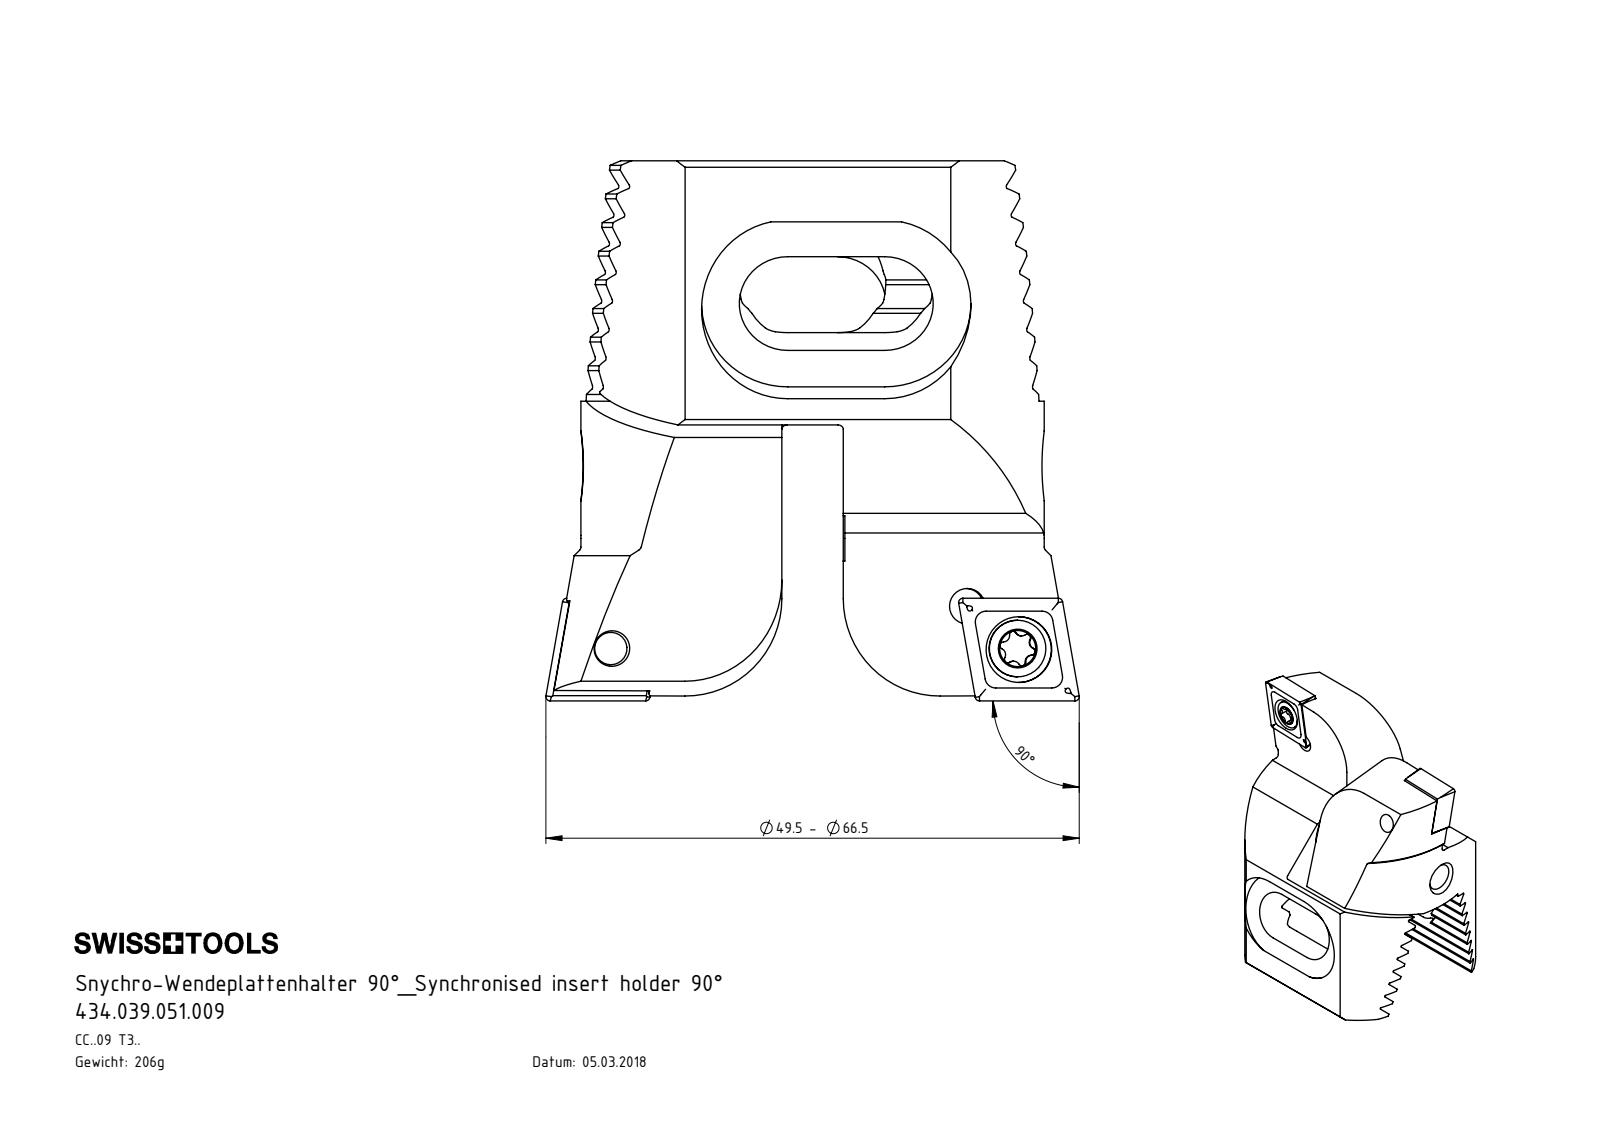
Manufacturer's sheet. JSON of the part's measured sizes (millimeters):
{"part_name": "Z42-ER3.001.040_A; Z42-ER3.000.040; 434.039.051.009; Z42-ER3.002.005_A (+4 more)", "step_written_by": "SolidWorks 2017 (CONFIG_CONTROL_DESIGN)", "units": "millimeters", "bodies": {"solids": 11, "faces": 525, "planar": 205, "cylindrical": 170, "other": 150}, "overall_size": [50.1, 49.5, 34.2], "volume_mm3": 27942, "surface_area_mm2": 14559, "round_holes": [[3.3, 7], [1, 2], [4.4, 2], [6.1, 2], [5, 1]], "round_bosses_or_shafts": [[3, 3], [5.25, 2], [4, 2], [17, 1], [6, 1], [3.8, 1]], "partial_cylinders_radius": [[0.2, 16], [0.34, 12], [0.59, 12], [1, 8], [0.5, 4], [4.5, 4], [8, 4], [9, 2]], "face_to_face_distances": [2.38, 4.76, 11.91, 9.53, 14.29, 7.15, 4.99, 7.14, 1.04, 16.67], "hole_center_spacings": [6.1, 13, 33.59, 6.25, 6.26, 25.12, 28.69, 33.71]}
